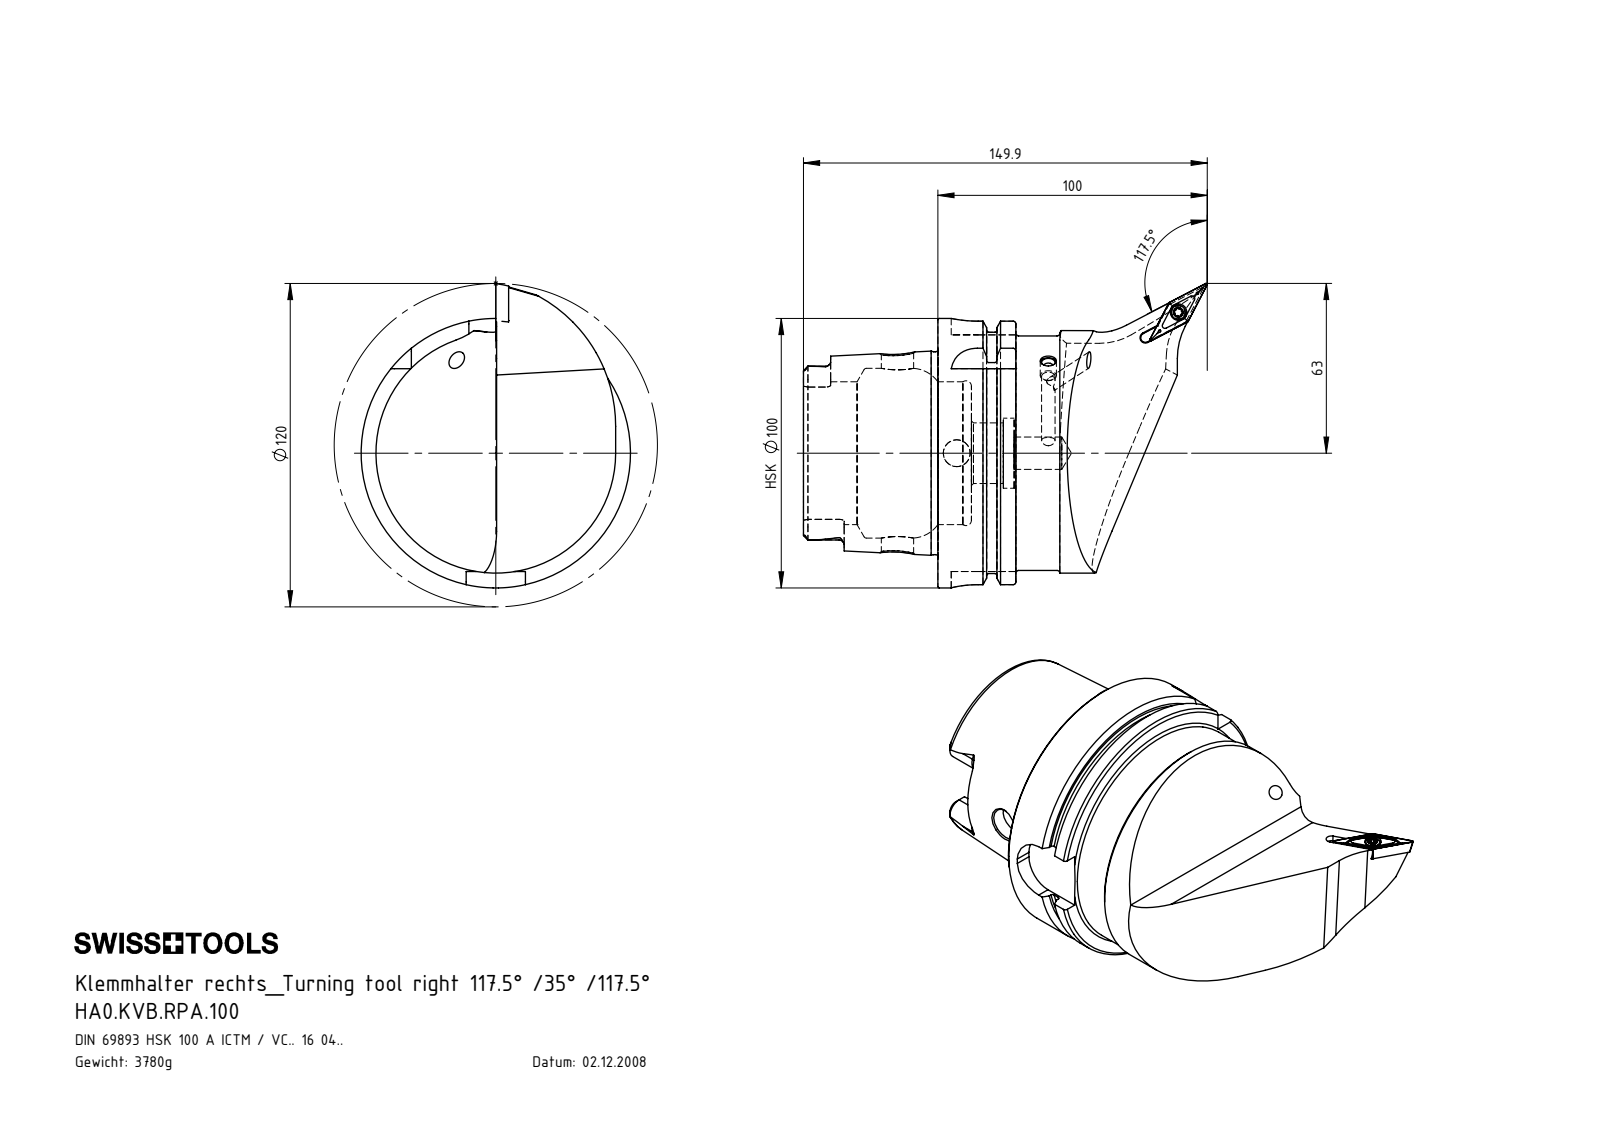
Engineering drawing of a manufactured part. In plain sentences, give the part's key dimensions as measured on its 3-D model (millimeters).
The part is named "HA0-KVB.RPA.100_A_Fertigbearbeitung; VCMT160404; KVT_MB_600_050; HA0.KVB.RPA.100 (+1 more)". Its 3-D file was written by "SolidWorks 2009 (CONFIG_CONTROL_DESIGN)". It is 5 solids with 314 faces: 79 planar, 89 cylindrical and 146 other. Overall it measures 149.92 by 113.02 by 100 millimeters. Its volume is 499 693 cubic millimeters and its surface area 66 076 square millimeters. Round holes: 2 of diameter 4.2, 2 of diameter 12, 1 of diameter 3.3, 1 of diameter 4, 1 of diameter 4.4, 1 of diameter 6.1, 1 of diameter 10, 1 of diameter 22.5, 1 of diameter 26, 1 of diameter 53, 1 of diameter 63. Round bosses or shafts: 1 of diameter 100, 1 of diameter 91.95, 1 of diameter 87, 1 of diameter 75.26, 1 of diameter 5.25, 1 of diameter 5, 1 of diameter 4. Partial cylindrical surfaces (rounded edges, fillets, slot ends): 6 of radius 0.34, 6 of radius 0.59, 6 of radius 1.9, 4 of radius 10, 2 of radius 4.83, 2 of radius 4.88, 1 of radius 1.75, 1 of radius 6. The main face-to-face distances are 12.45, 28.95, 16.5, 49.9, 62.35, 78.85, 87.8, 78.2, 28.3, 15.85. The hole center spacings are 97.46, 97.57.
